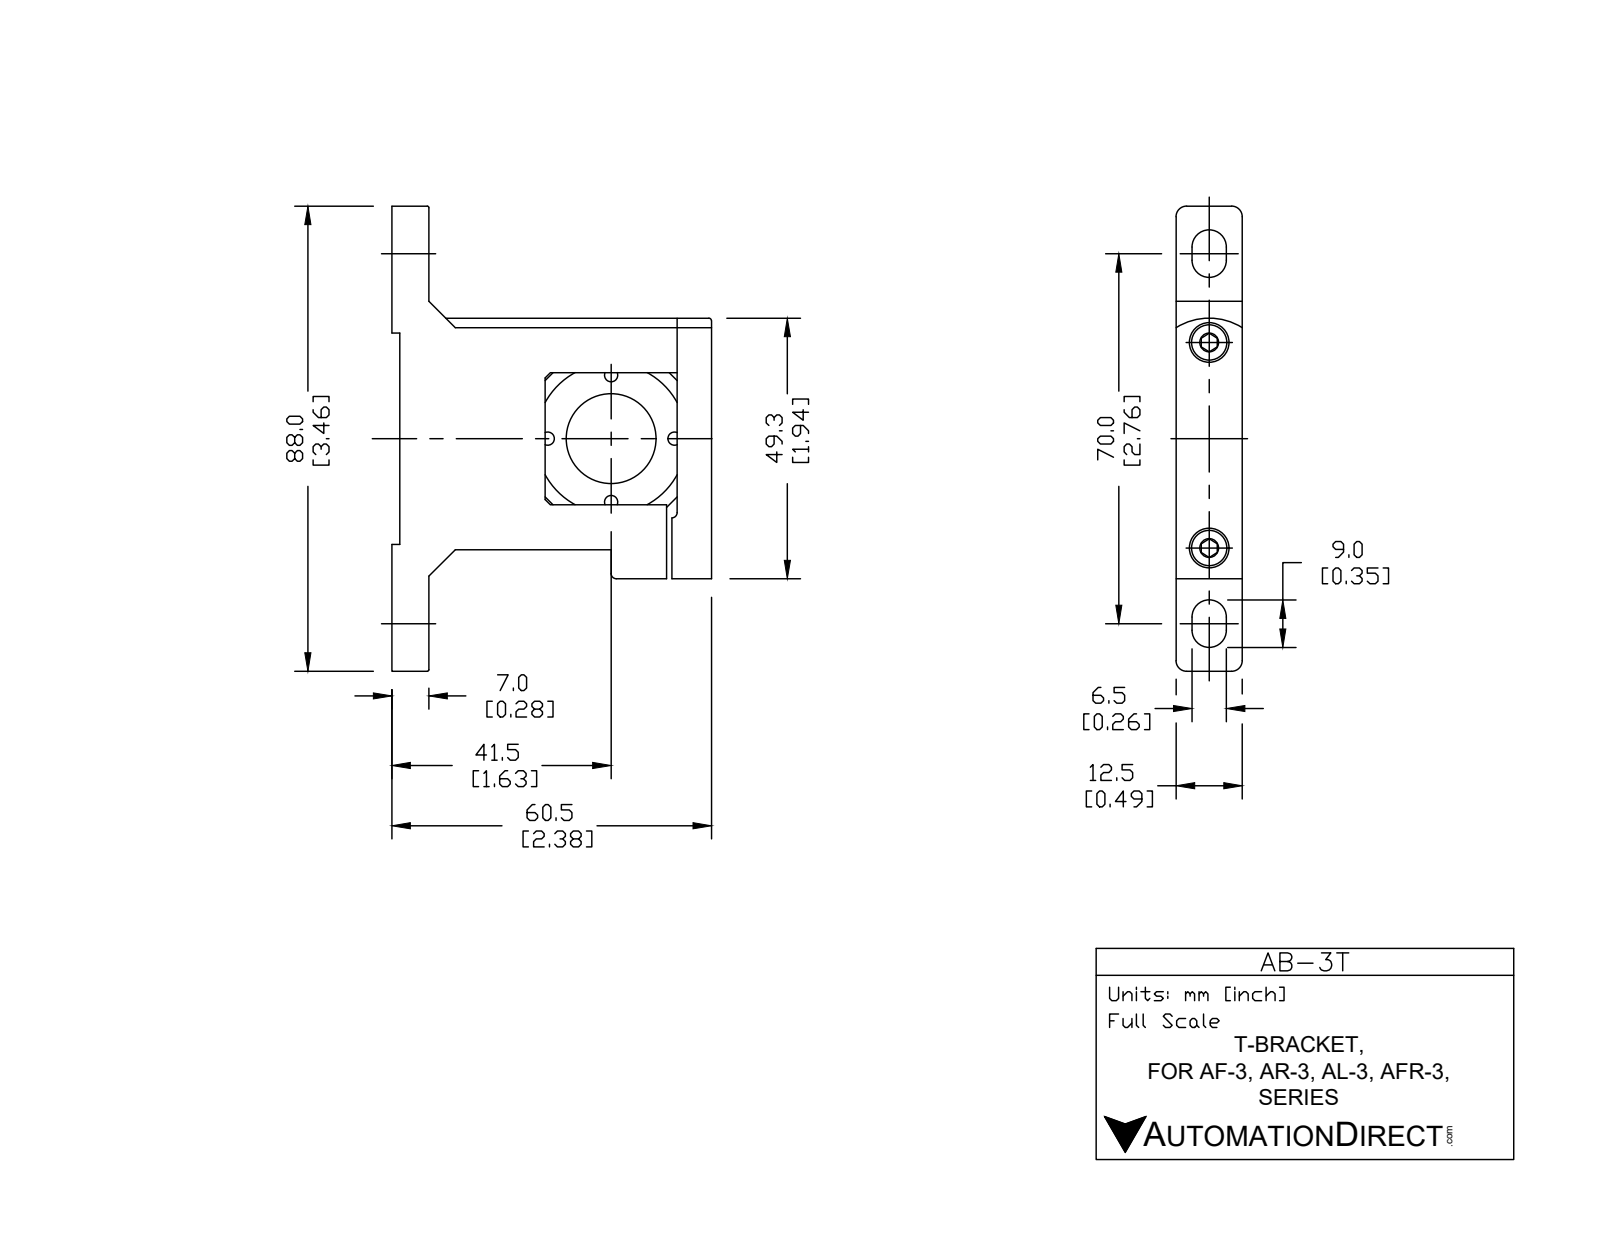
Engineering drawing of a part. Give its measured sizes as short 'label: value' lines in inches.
name: AB-3T
written by: SolidWorks 2015 (CONFIG_CONTROL_DESIGN)
unit: in
bodies: 3 solids, 110 faces (74 planar, 24 cylindrical, 12 other)
size: 3.465 × 2.382 × 0.492
volume: 1.734 in³; area: 19.57 in²
holes: 2× ⌀0.177, 2× ⌀0.244, 1× ⌀0.669
bosses: 2× ⌀0.226, 2× ⌀0.157
rounds: 4× R0.128, 1× R0.059, 1× R0.463
face distances: 0.492, 0.079, 1.063, 1.142, 2.382, 0.256, 0.049, 2.333, 0.413, 0.226
hole spacings: 1.531
